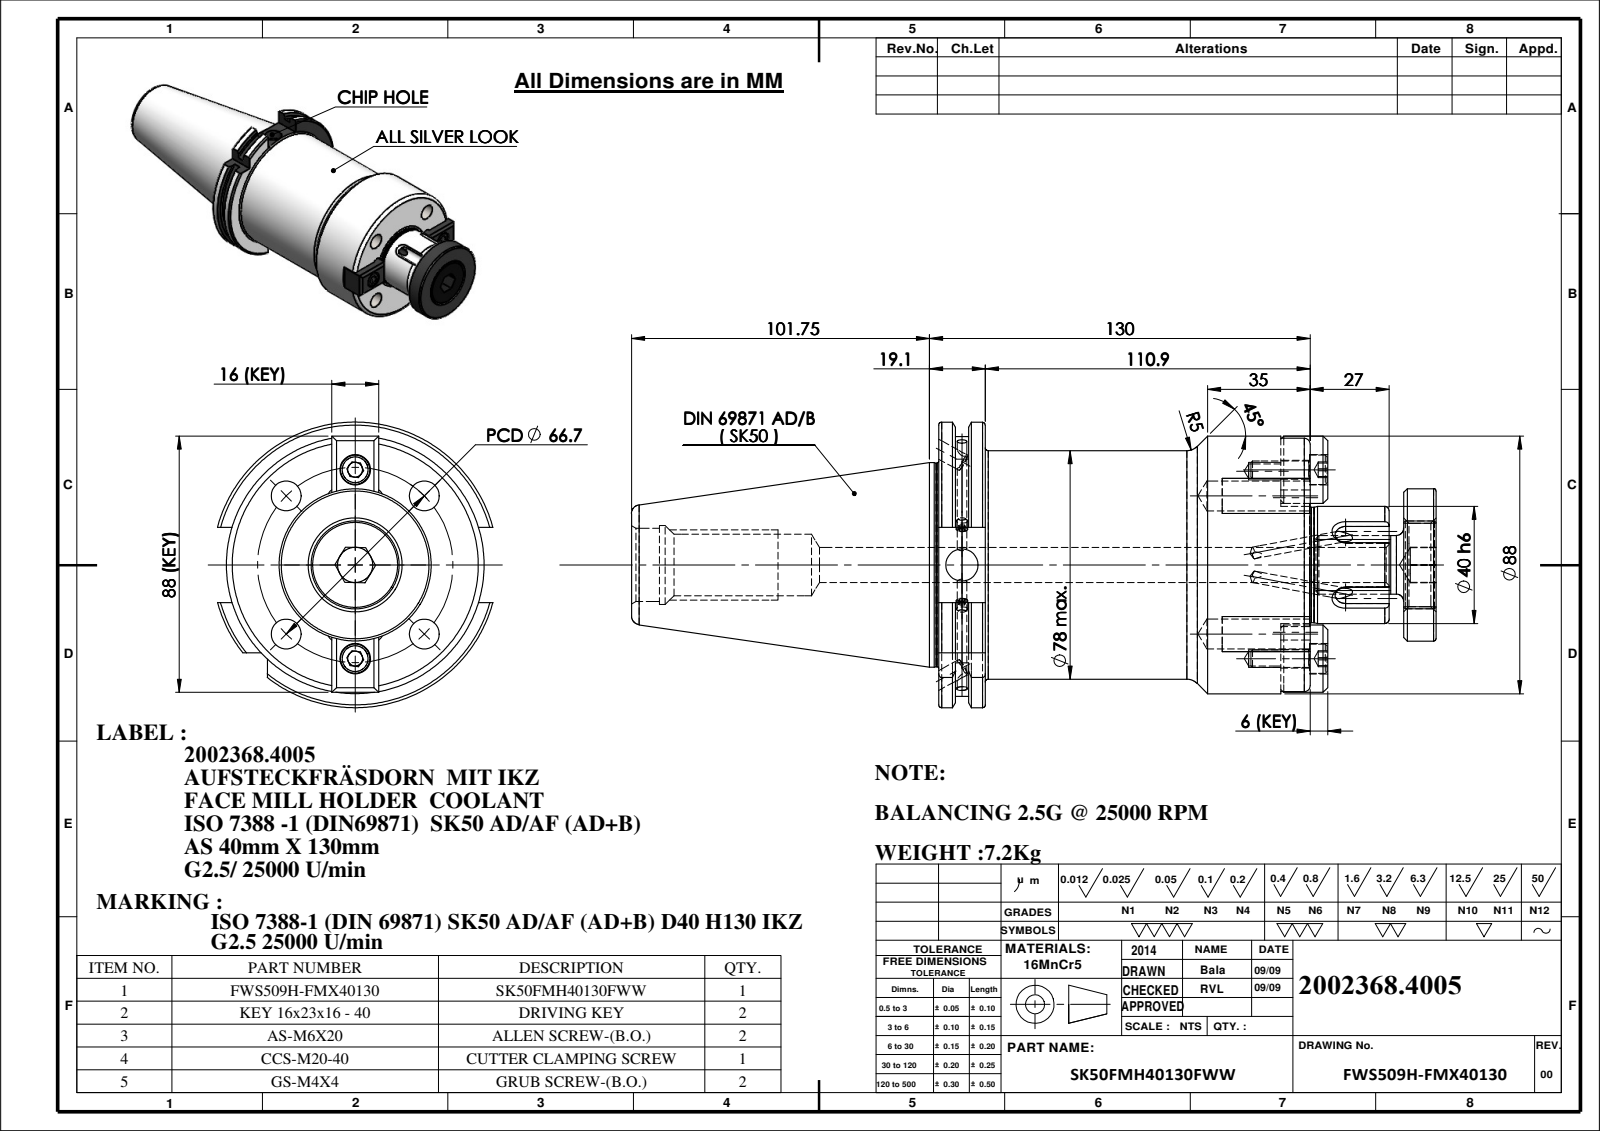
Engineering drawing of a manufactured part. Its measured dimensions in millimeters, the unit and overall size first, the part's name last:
Units: millimetres
Overall size (bounding box): 274.75 × 97.5 × 94.05
Round holes (diameter × count): ⌀4 ×4, ⌀10.2 ×4, ⌀5 ×2, ⌀6 ×2, ⌀6.4 ×2, ⌀10.4 ×2, ⌀3.3 ×1, ⌀11 ×1, ⌀12 ×1, ⌀21 ×1, ⌀25 ×1, ⌀27 ×1
Round bosses / shafts (diameter × count): ⌀10 ×2, ⌀6 ×2, ⌀88 ×1, ⌀78 ×1, ⌀69.85 ×1, ⌀69.45 ×1, ⌀52 ×1, ⌀40 ×1
Partial cylindrical surfaces — rounded edges, fillets, slot ends (radius × count): R3 ×4, R4 ×4, R44.9 ×1, R48.75 ×1
Main face-to-face distances: 126.8, 16, 15.9, 110.9, 169.8, 153.9, 43, 42, 158.8, 142.9
Hole centre spacings: 25.04, 33.35, 47.16, 60.38, 25.21, 32, 60.84, 66.69
Volume: 948 571 mm³ · Surface area: 105 898 mm²
Bodies: 9 solids, 378 faces (139 planar, 109 cylindrical, 130 other)
Part name (STEP PRODUCT): SK50FMH40130FWW; CCS-M20-40-2; KEY 16x23x16 - 40; CCS-M20-40 (+4 more)
STEP written by: SolidWorks 2018 (CONFIG_CONTROL_DESIGN)
